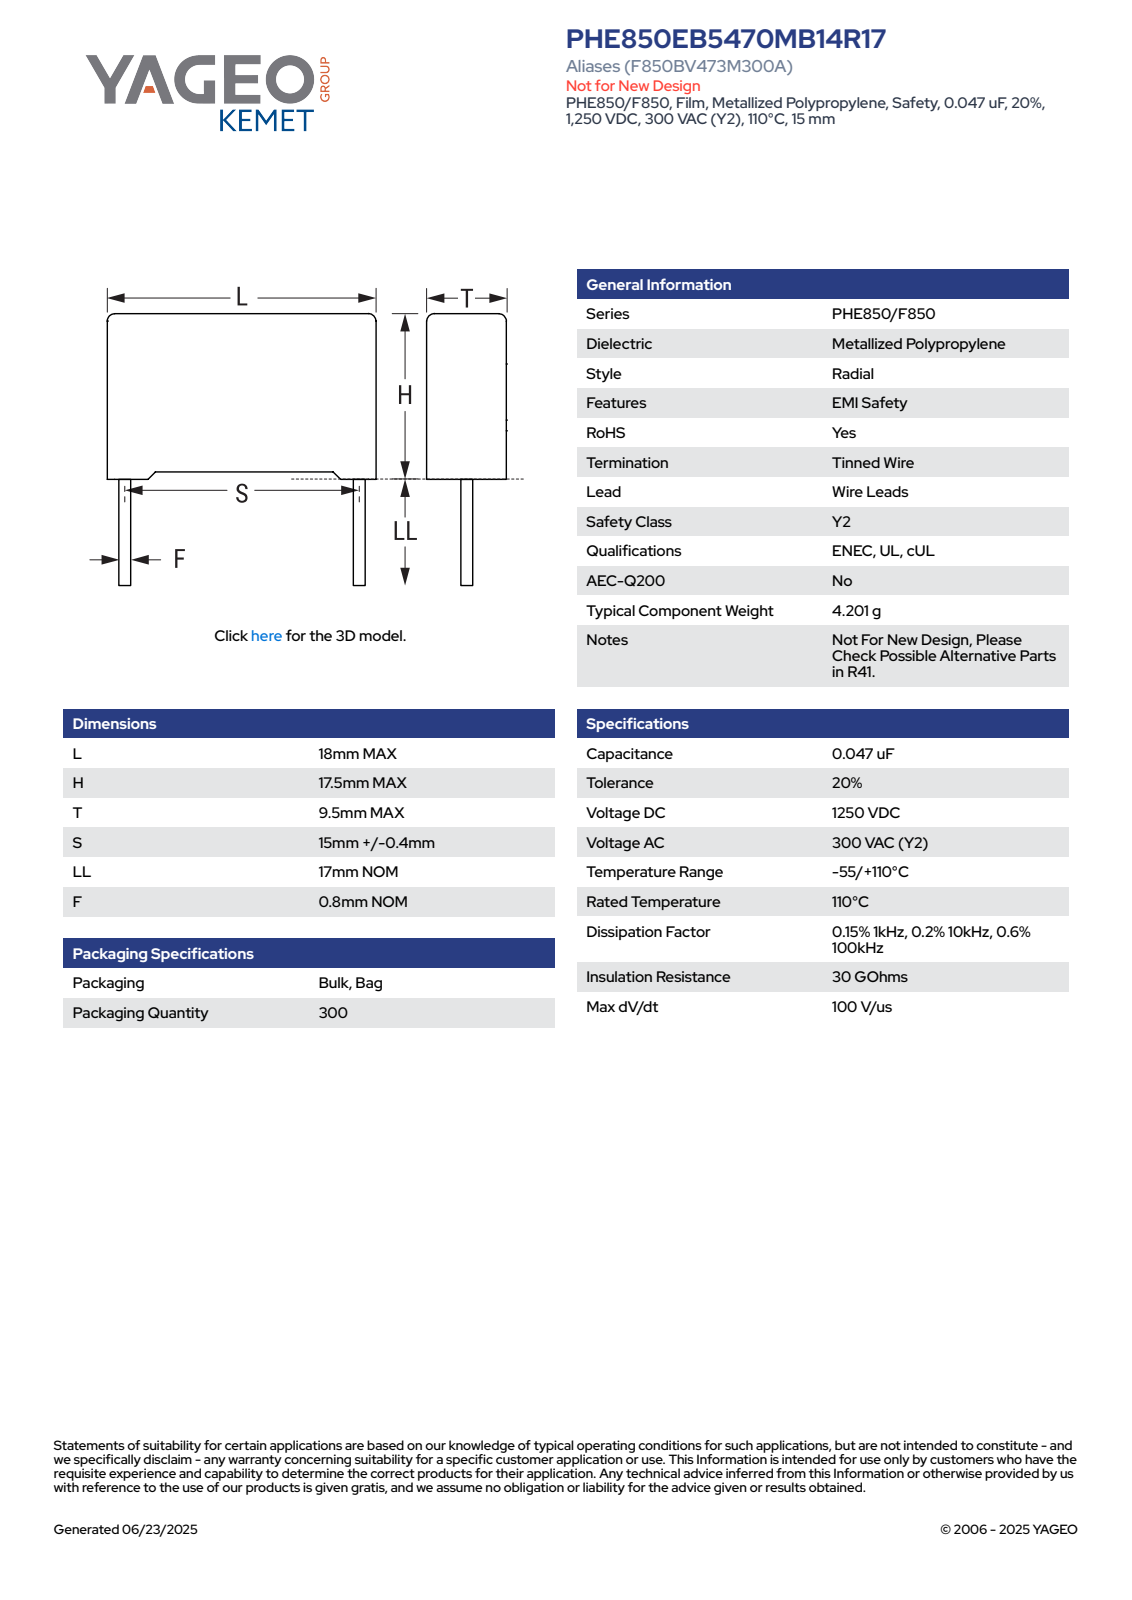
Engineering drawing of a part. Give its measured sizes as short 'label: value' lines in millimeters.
name: CFR_RB2_18X17.5X9.5_L18H17.5T9.5S15LL17F0.8
written by: SolidWorks 2021 (AUTOMOTIVE_DESIGN)
unit: mm
bodies: 4 solids, 85 faces (77 planar, 8 cylindrical, 0 other)
size: 34.5 × 18 × 9.51
volume: 2 895 mm³; area: 1 417 mm²
bosses: 2× ⌀0.8
rounds: 4× R0.5
face distances: 9.5, 18, 16.75, 0.6, 0.75, 17.5, 16.9, 17.4, 8.9, 16.8
